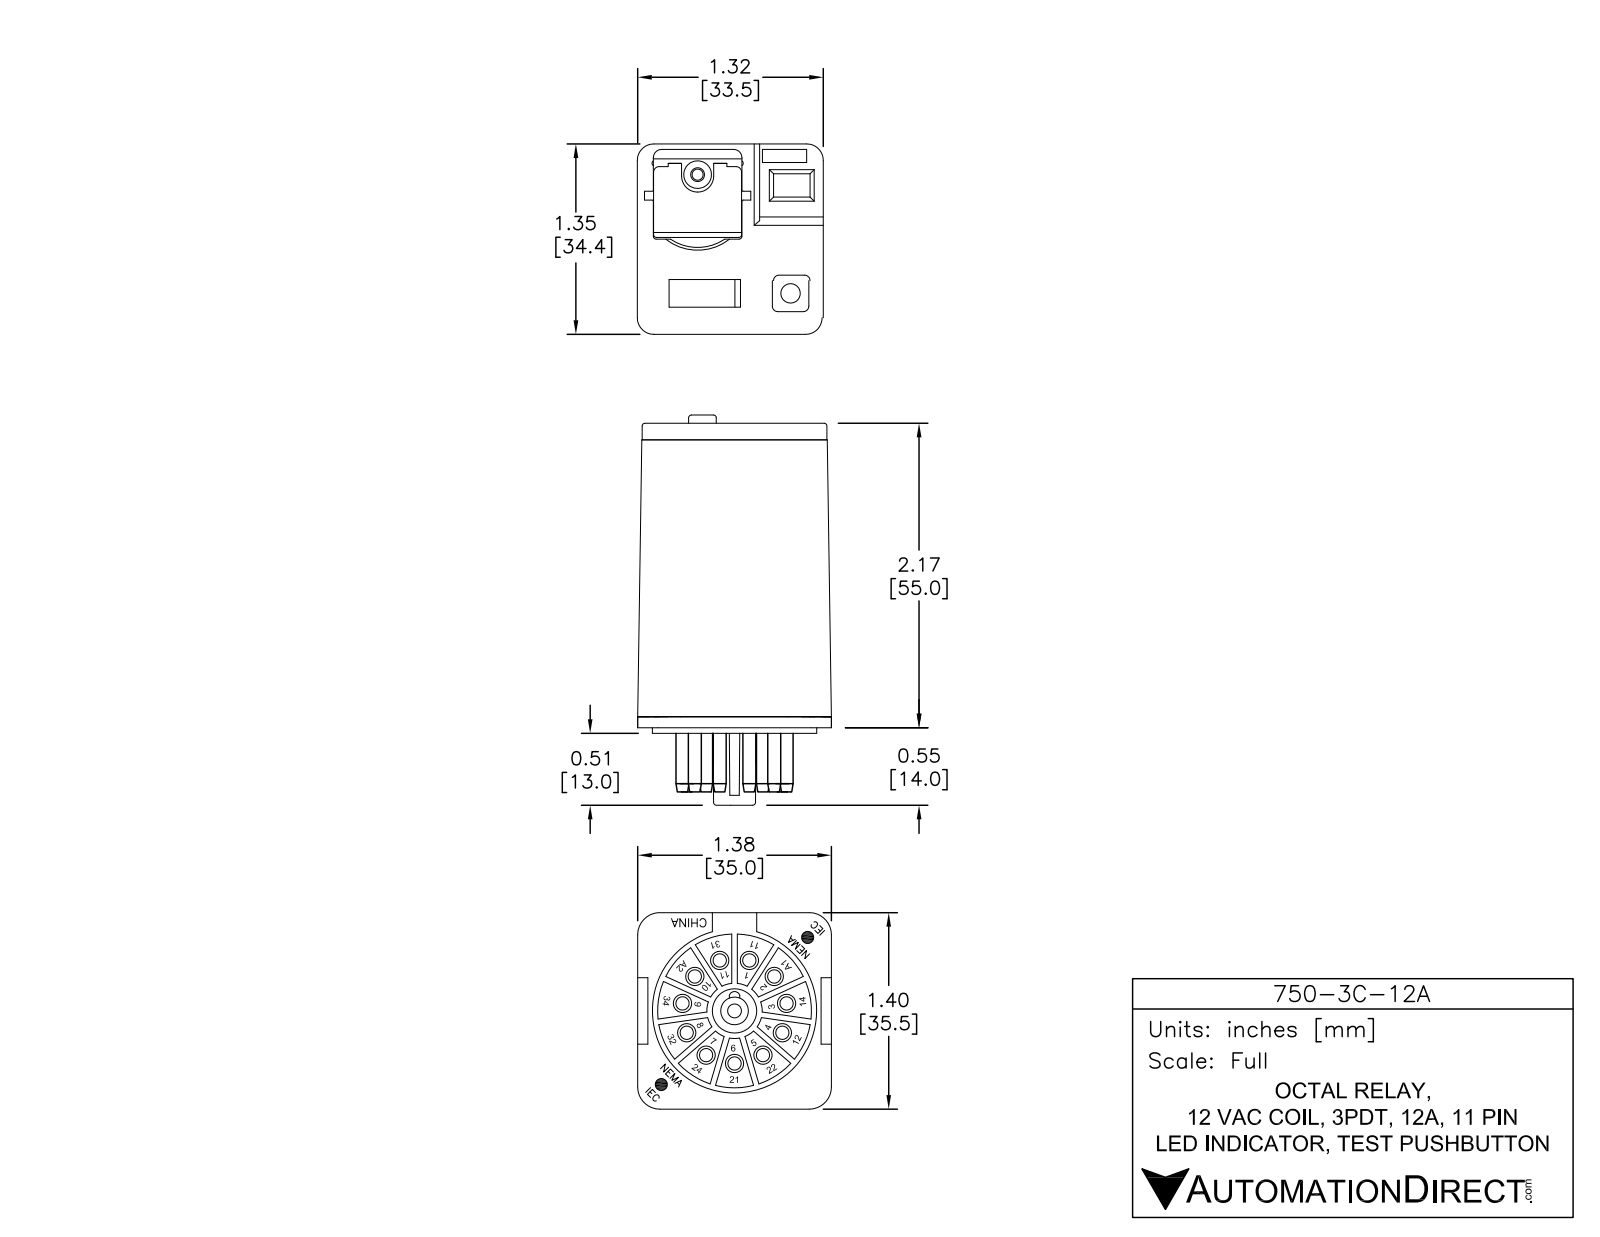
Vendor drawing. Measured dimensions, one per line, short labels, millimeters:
name: 750-3C-12D
written by: SolidWorks 2013 (AUTOMOTIVE_DESIGN)
unit: mm
bodies: 5 solids, 392 faces (194 planar, 104 cylindrical, 94 other)
size: 69.6 × 35.12 × 35
volume: 67 626 mm³; area: 16 685 mm²
holes: 1× ⌀2.5
bosses: 11× ⌀3, 11× ⌀2.2, 1× ⌀29.5, 1× ⌀8, 1× ⌀4.8, 1× ⌀0.83
rounds: 4× R0.5, 4× R3, 2× R0.25, 2× R1, 1× R0.75, 1× R0.99, 1× R2.5, 1× R5
face distances: 35, 50, 54.75, 3, 53, 1.75, 51.75, 1, 53.35, 1.4
